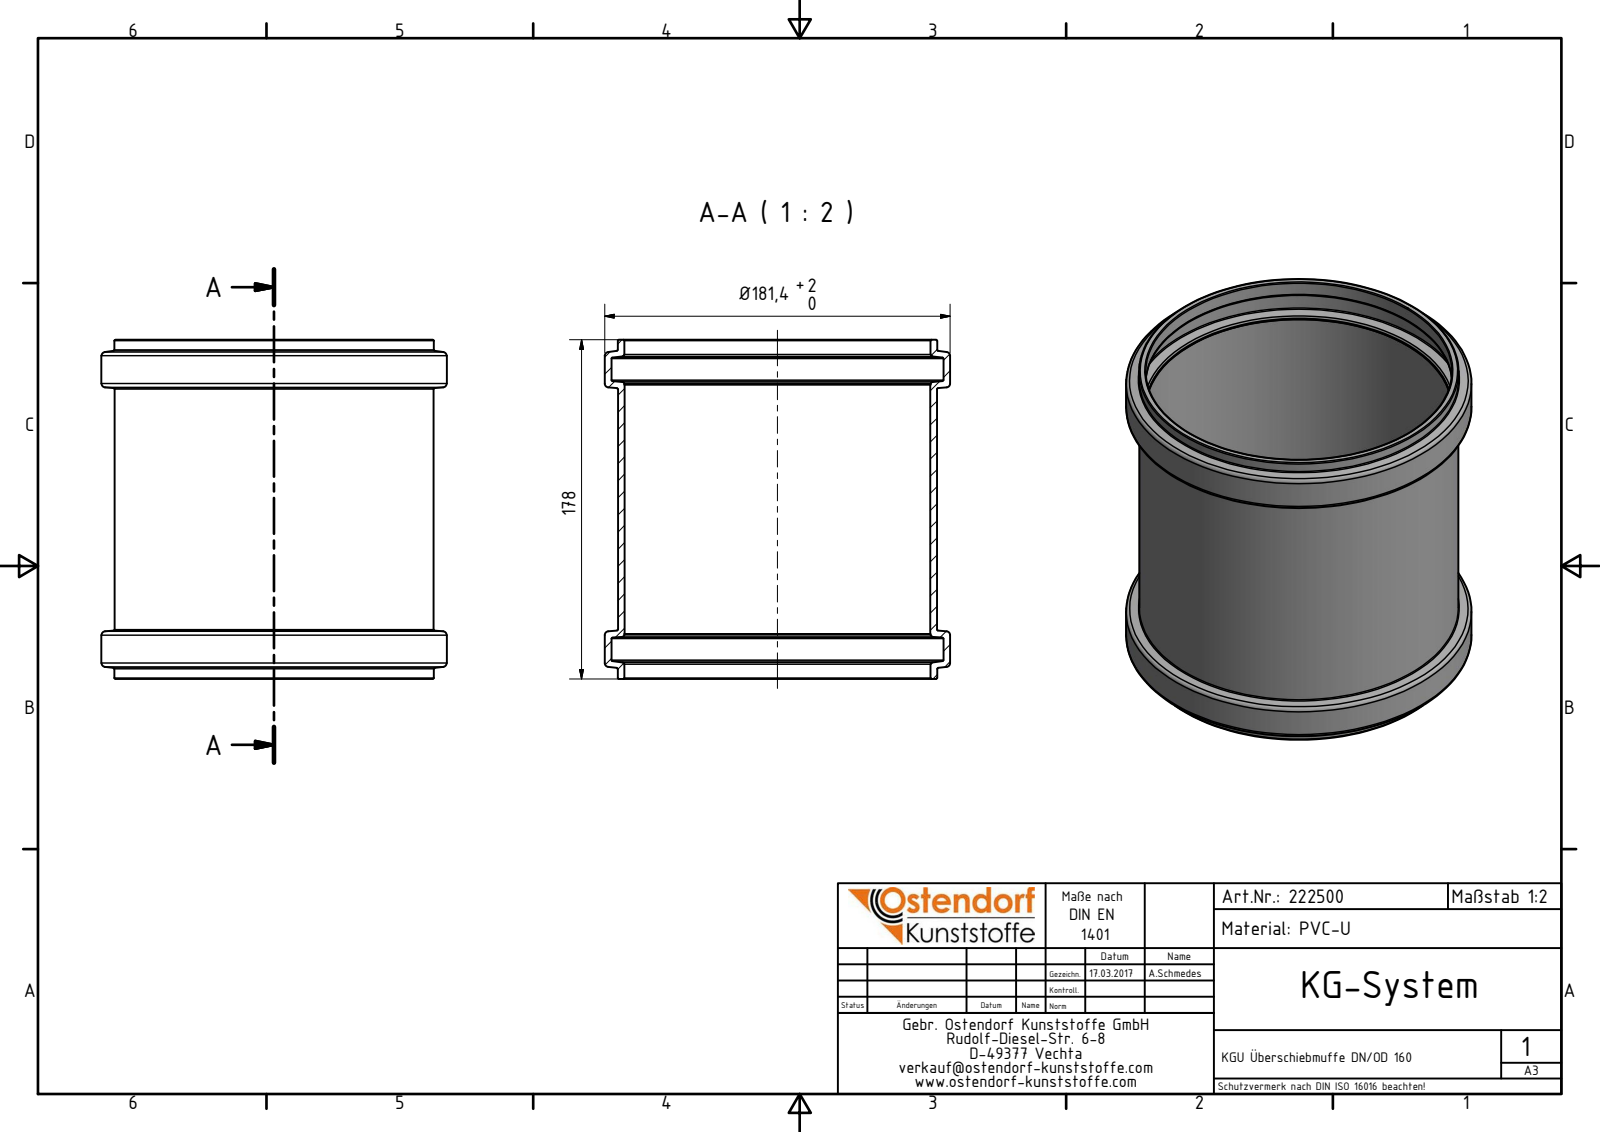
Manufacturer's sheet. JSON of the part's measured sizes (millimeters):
{"part_name": "222500 KGU Überschiebmuffe DN_OD 160", "step_written_by": "Autodesk Inventor 2016 (AUTOMOTIVE_DESIGN)", "units": "millimeters", "bodies": {"solids": 1, "faces": 44, "planar": 4, "cylindrical": 12, "other": 28}, "overall_size": [181.4, 181.4, 178], "volume_mm3": 368274, "surface_area_mm2": 213107, "round_holes": [[160.5, 1], [160.8, 1], [174.4, 1]], "round_bosses_or_shafts": [[181.4, 1], [167.8, 1], [167.5, 1]], "face_to_face_distances": [178, 23.63, 154.37, 130.74]}
